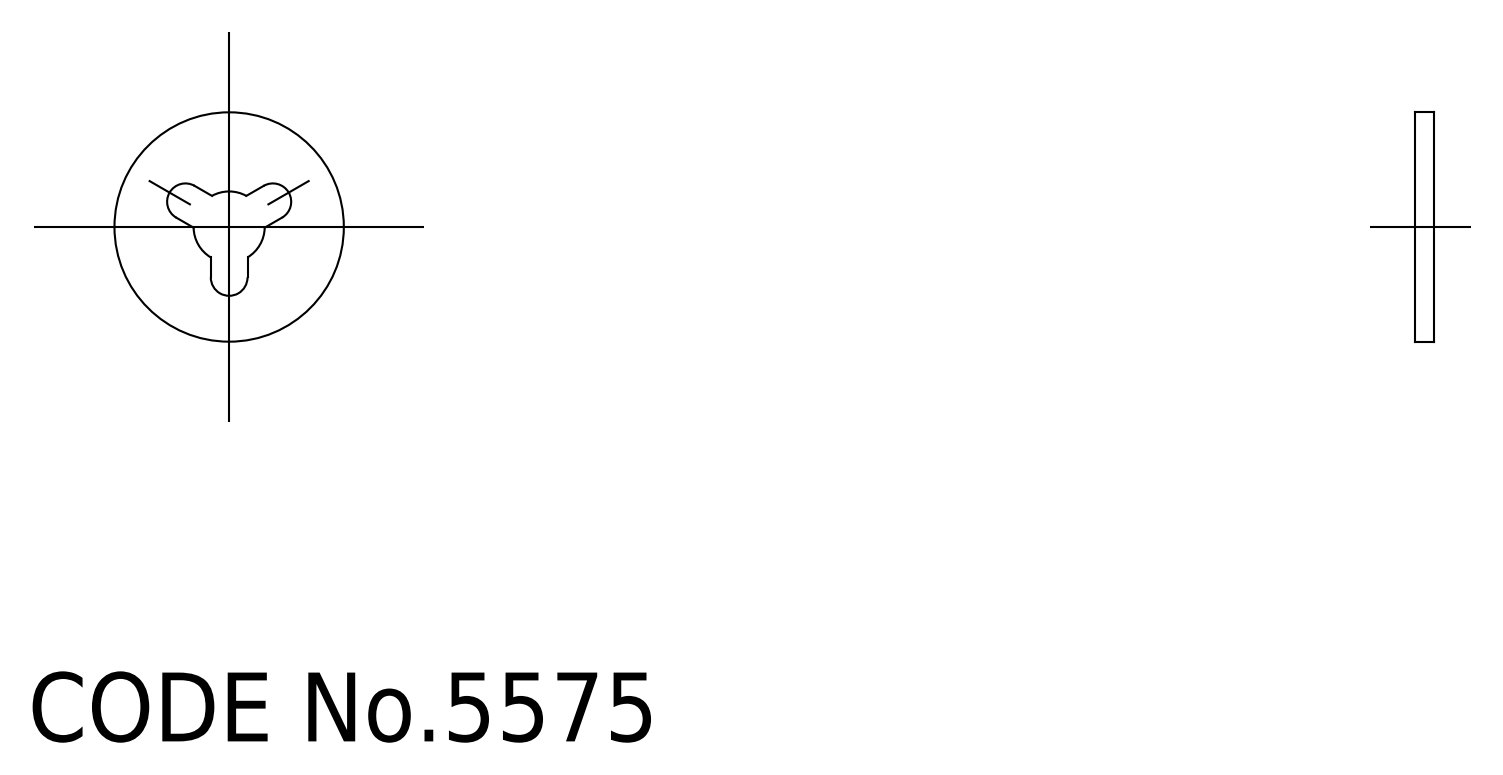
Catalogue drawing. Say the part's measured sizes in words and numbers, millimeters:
The part is named "washer". Its 3-D file was written by "CADfix (AUTOMOTIVE_DESIGN)". It is 1 solid with 16 faces: 0 planar, 0 cylindrical and 16 other. Overall it measures 10 by 10 by 0.8 millimeters. Its volume is 52 cubic millimeters and its surface area 168 square millimeters.
